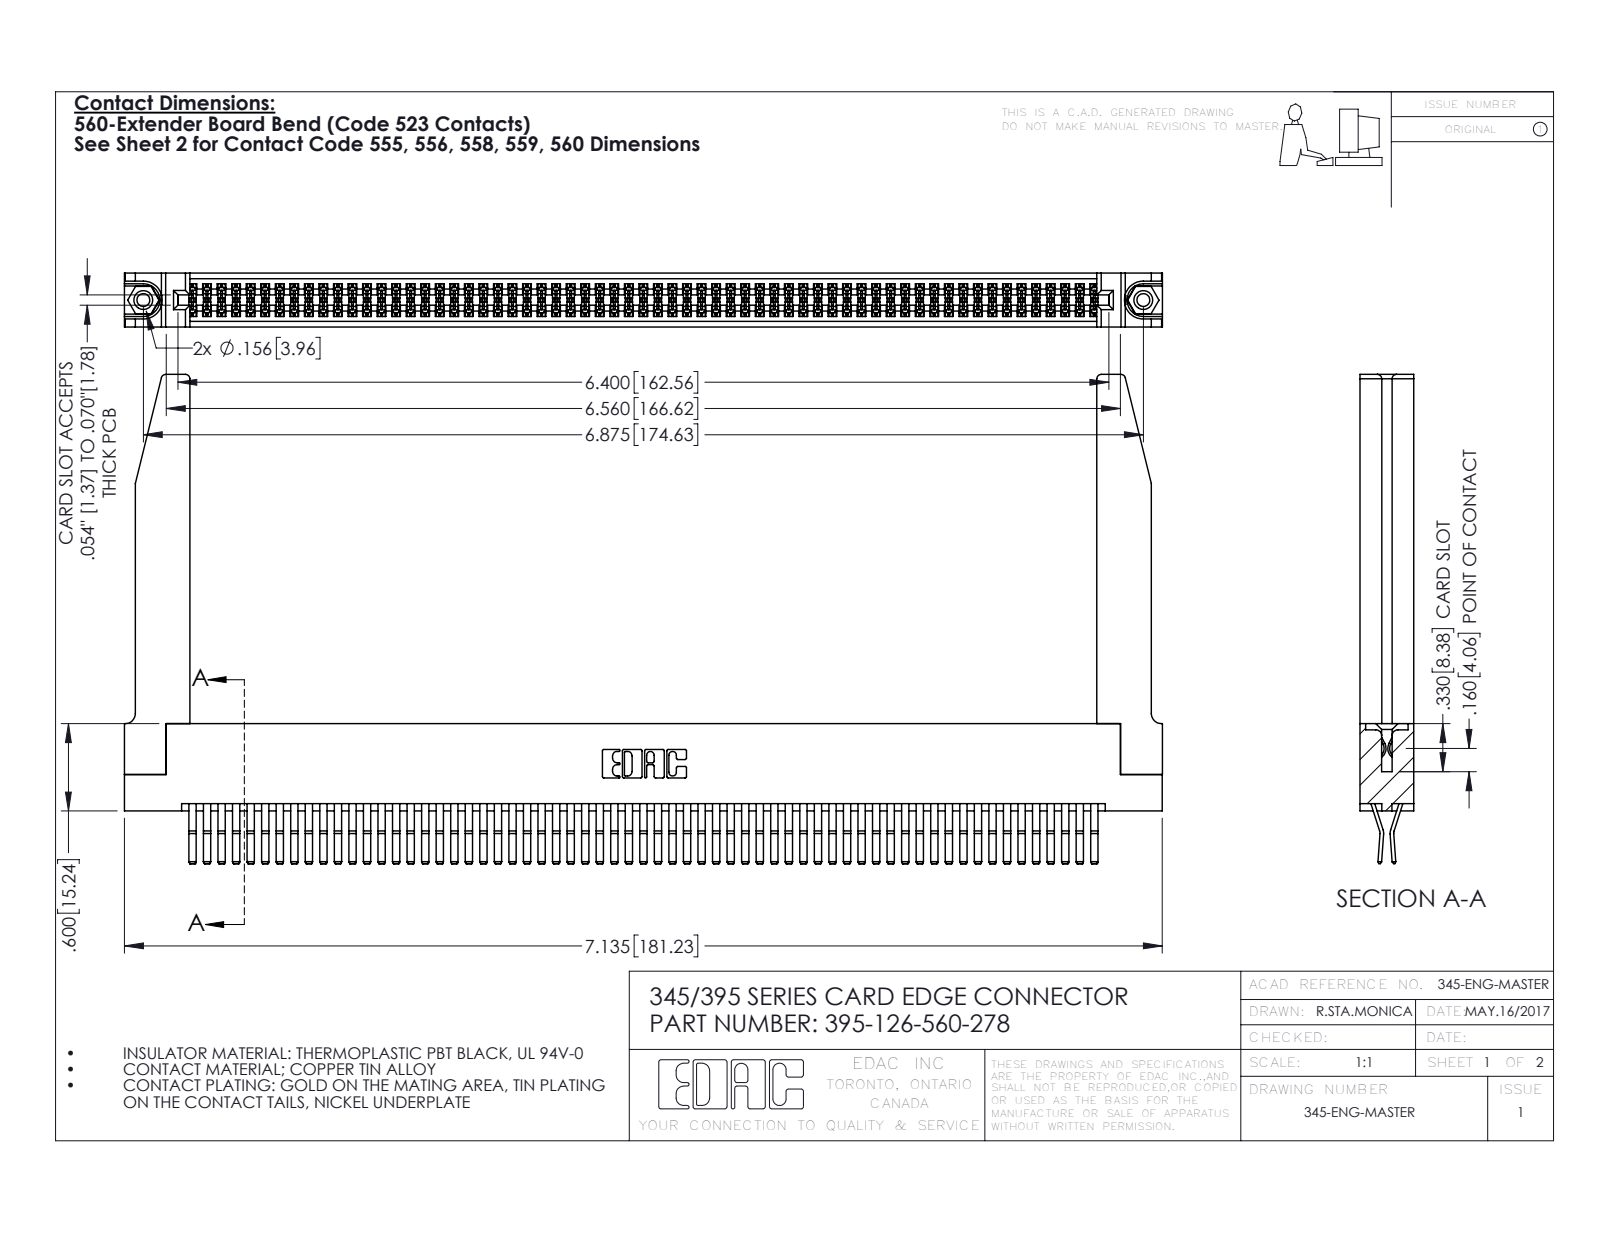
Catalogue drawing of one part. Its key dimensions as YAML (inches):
part_name: "345 Part_Flush Mounting Lugs - 0.156 Dia-TH; 345-220-078_345-220-078; 345-292-001_560 Tail; 345-250-001_345-250-001-102 (+1 more)"
step_written_by: "SolidWorks 2016 (CONFIG_CONTROL_DESIGN)"
units: inches
bodies: {solids: 131, faces: 6912, planar: 4380, cylindrical: 2480, other: 52}
overall_size: [7.136, 3.362, 0.37]
volume: 1.611
surface_area: 57.2
round_holes:
  - {diameter: 0.089, count: 2}
  - {diameter: 0.125, count: 2}
  - {diameter: 0.156, count: 2}
  - {diameter: 0.064, count: 1}
round_bosses_or_shafts:
  - {diameter: 0.155, count: 2}
partial_cylinders:
  - {radius: 0.006, count: 190}
  - {radius: 0.01, count: 22}
  - {radius: 0.03, count: 8}
  - {radius: 0.007, count: 6}
  - {radius: 0.031, count: 6}
  - {radius: 0.026, count: 3}
  - {radius: 0.01, count: 2}
  - {radius: 0.014, count: 2}
face_to_face_distances: [0.072, 0.298, 0.025, 0.37, 0.2, 0.098, 0.272, 0.225, 0.175, 0.148]
hole_center_spacings: [0.27, 6.639, 6.875]
